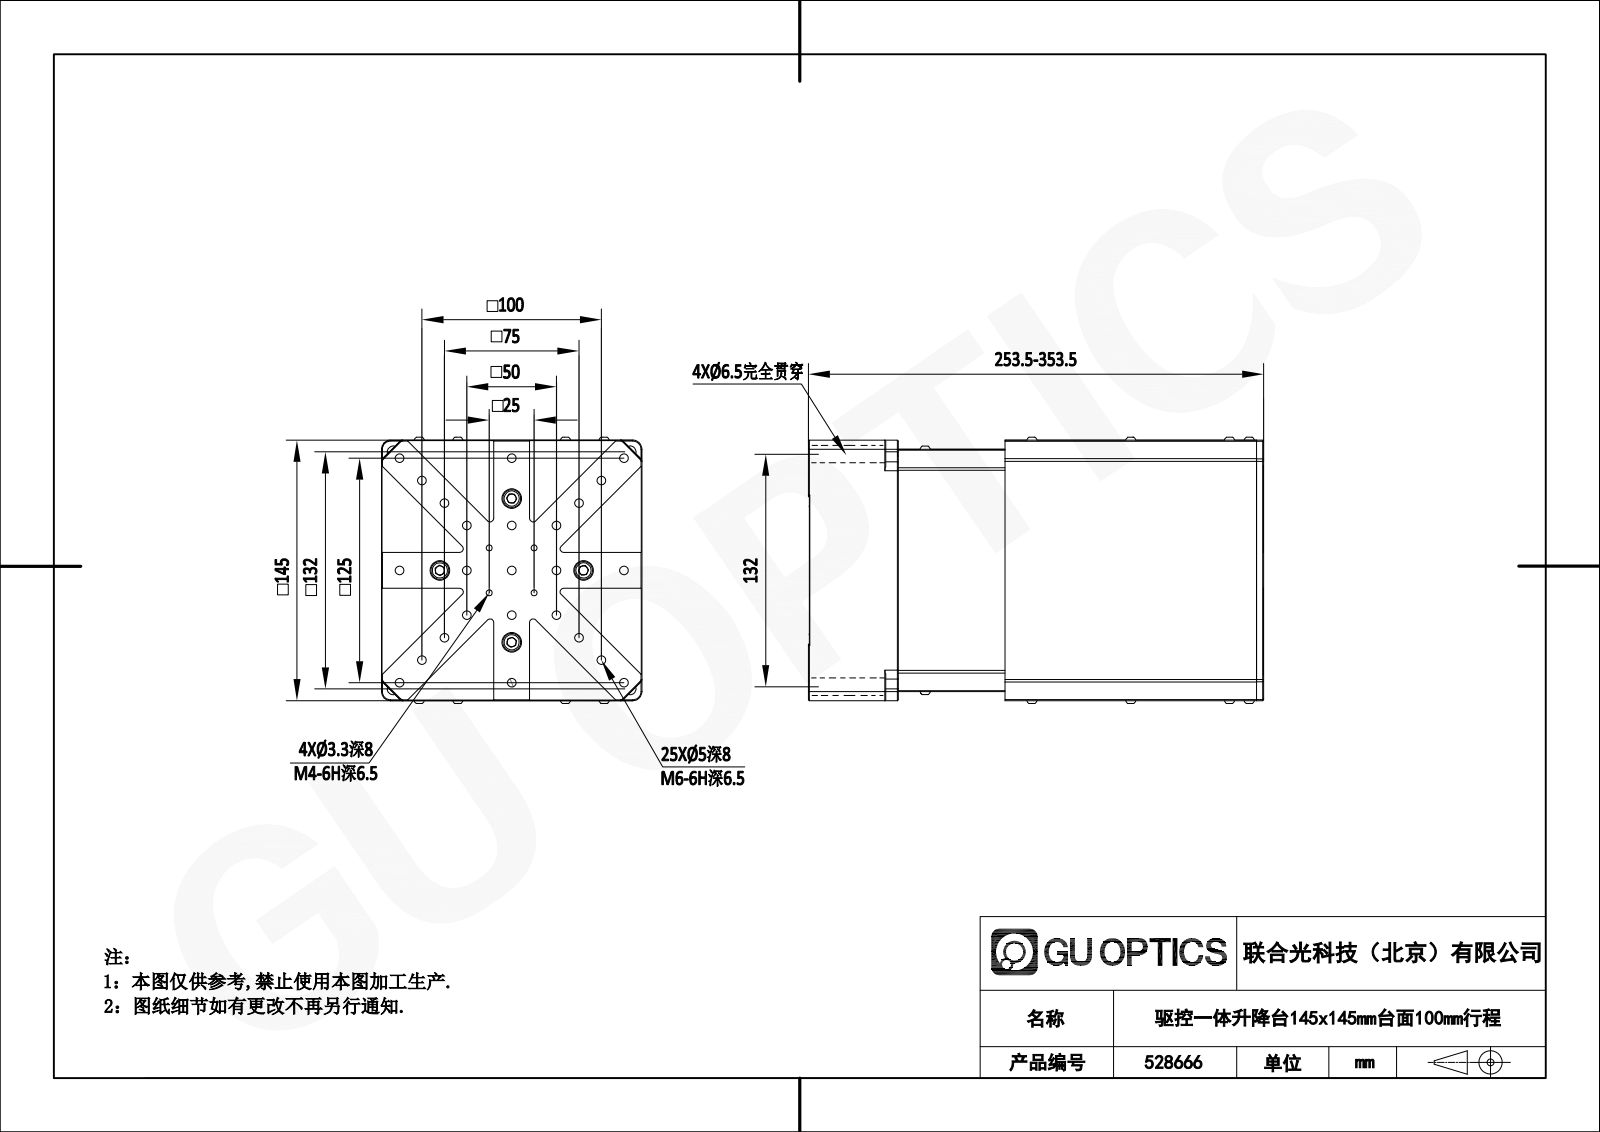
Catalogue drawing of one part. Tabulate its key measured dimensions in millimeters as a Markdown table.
| quantity | value |
| --- | --- |
| part name | 528666 |
| STEP written by | SolidWorks 2020 (CONFIG_CONTROL_DESIGN) |
| units | millimeters |
| bodies | 0 solids, 4330 faces (2236 planar, 1350 cylindrical, 744 other) |
| overall size | 253.5 × 148.3 × 145 |
| round holes (diameter × count) | 2.5 × 38, 5 × 37, 3.3 × 36, 4.5 × 32, 8 × 32, 1.5 × 18, 6.5 × 16, 1.6 × 10, 6.4 × 8, 11 × 8, 13 × 8, 18.66 × 8 |
| round bosses / shafts (diameter × count) | 2 × 22, 7 × 20, 4 × 20, 6 × 13, 10 × 12, 3 × 11, 3.8 × 10, 5.5 × 8 |
| partial cylindrical surfaces (radius × count) | 2 × 50, 1 × 24, 5 × 16, 5.5 × 4, 24 × 4, 25 × 4, 2.2 × 3, 13.5 × 1 |
| main face-to-face distances | 5, 1, 139, 140, 135, 6, 134, 4, 138, 144 |
| hole center spacings | 40, 16.5, 80, 43.27, 56.57, 23.5, 56.5, 23.33 |
